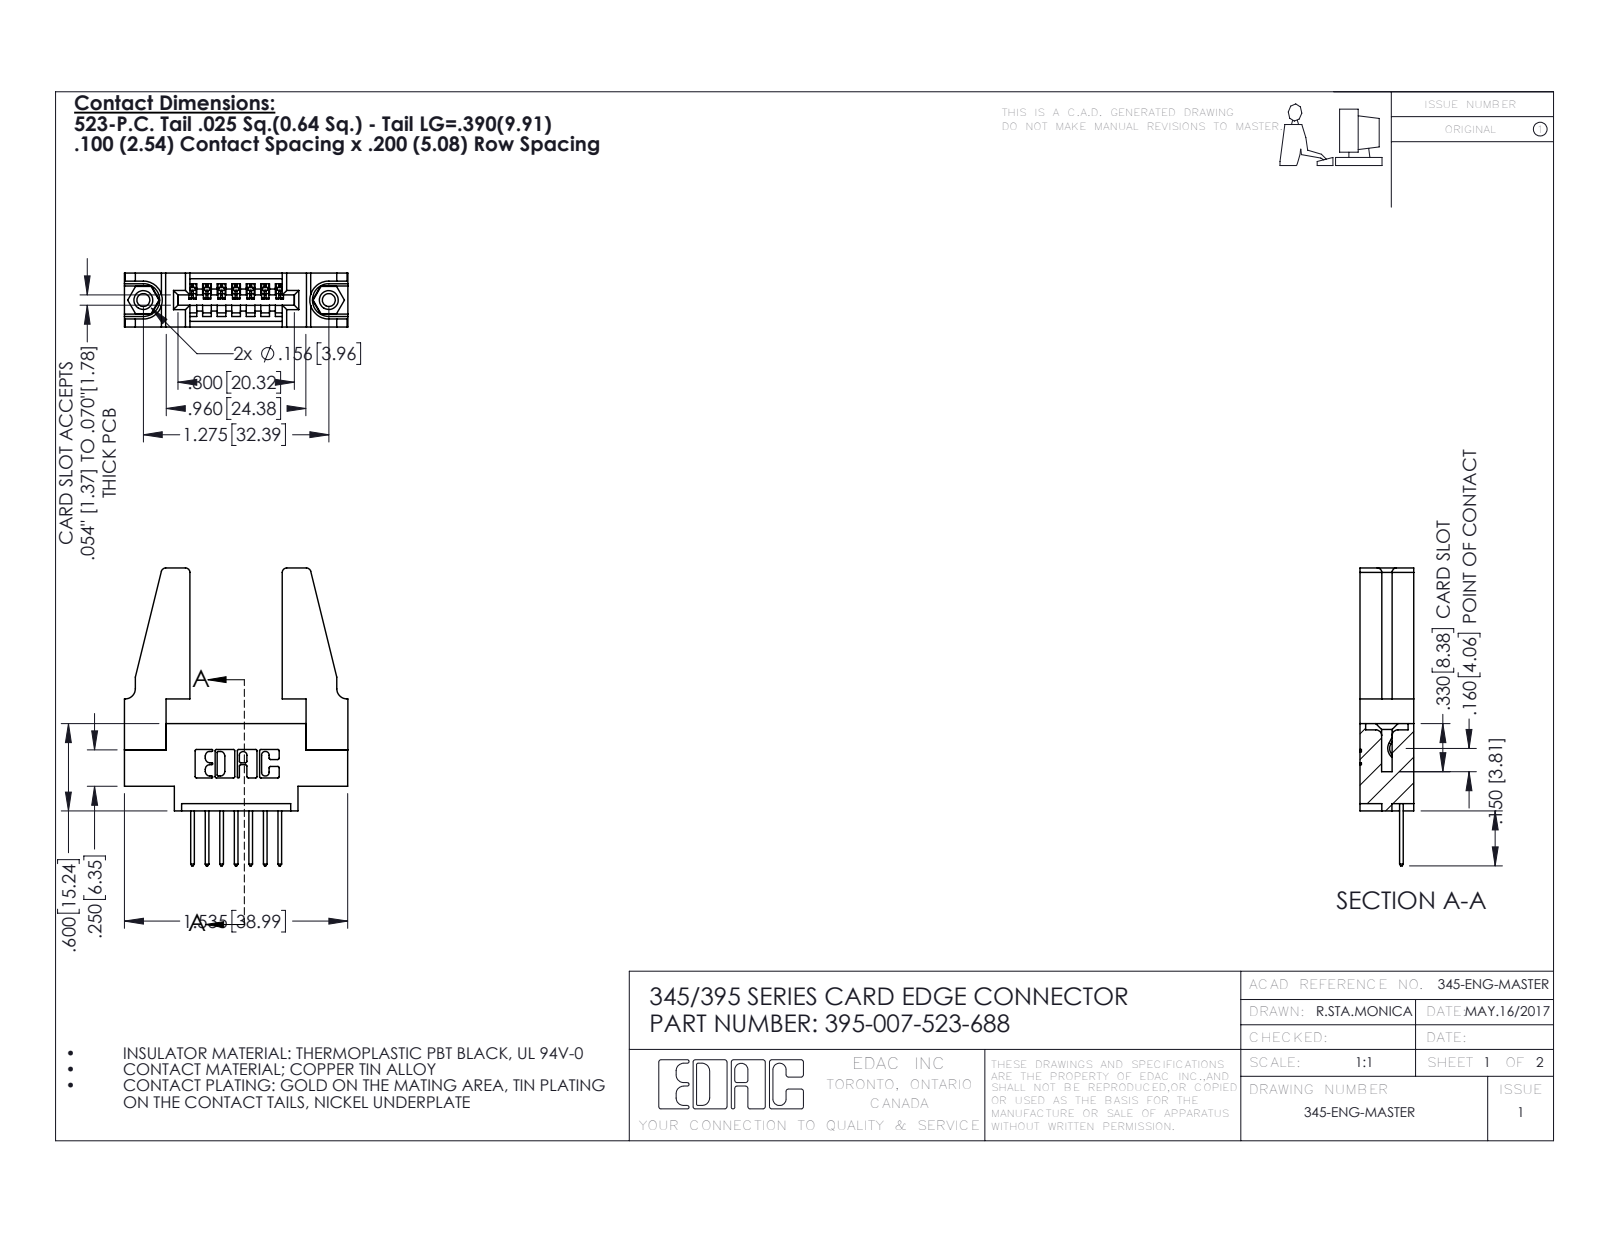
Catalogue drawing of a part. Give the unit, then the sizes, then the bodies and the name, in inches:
Units: inches
Overall size (bounding box): 2.047 × 1.536 × 0.37
Round holes (diameter × count): ⌀0.089 ×2, ⌀0.125 ×2, ⌀0.156 ×2, ⌀0.064 ×1
Round bosses / shafts (diameter × count): ⌀0.155 ×2
Partial cylindrical surfaces — rounded edges, fillets, slot ends (radius × count): R0.01 ×22, R0.006 ×14, R0.01 ×14, R0.03 ×8, R0.007 ×6, R0.031 ×6, R0.026 ×3, R0.031 ×2
Main face-to-face distances: 0.37, 0.072, 0.298, 0.2, 0.098, 0.272, 0.025, 0.148, 0.15, 0.22
Hole centre spacings: 0.27, 1.045, 1.275
Volume: 0.4 in³ · Surface area: 11.12 in²
Bodies: 12 solids, 660 faces (436 planar, 208 cylindrical, 16 other)
Part name (STEP PRODUCT): 395-007-523-688; 345-292-001_345-293-123; 345-220-078_345-220-088; 345-250-001_345-250-001-102 (+1 more)
STEP written by: SolidWorks 2016 (CONFIG_CONTROL_DESIGN)
